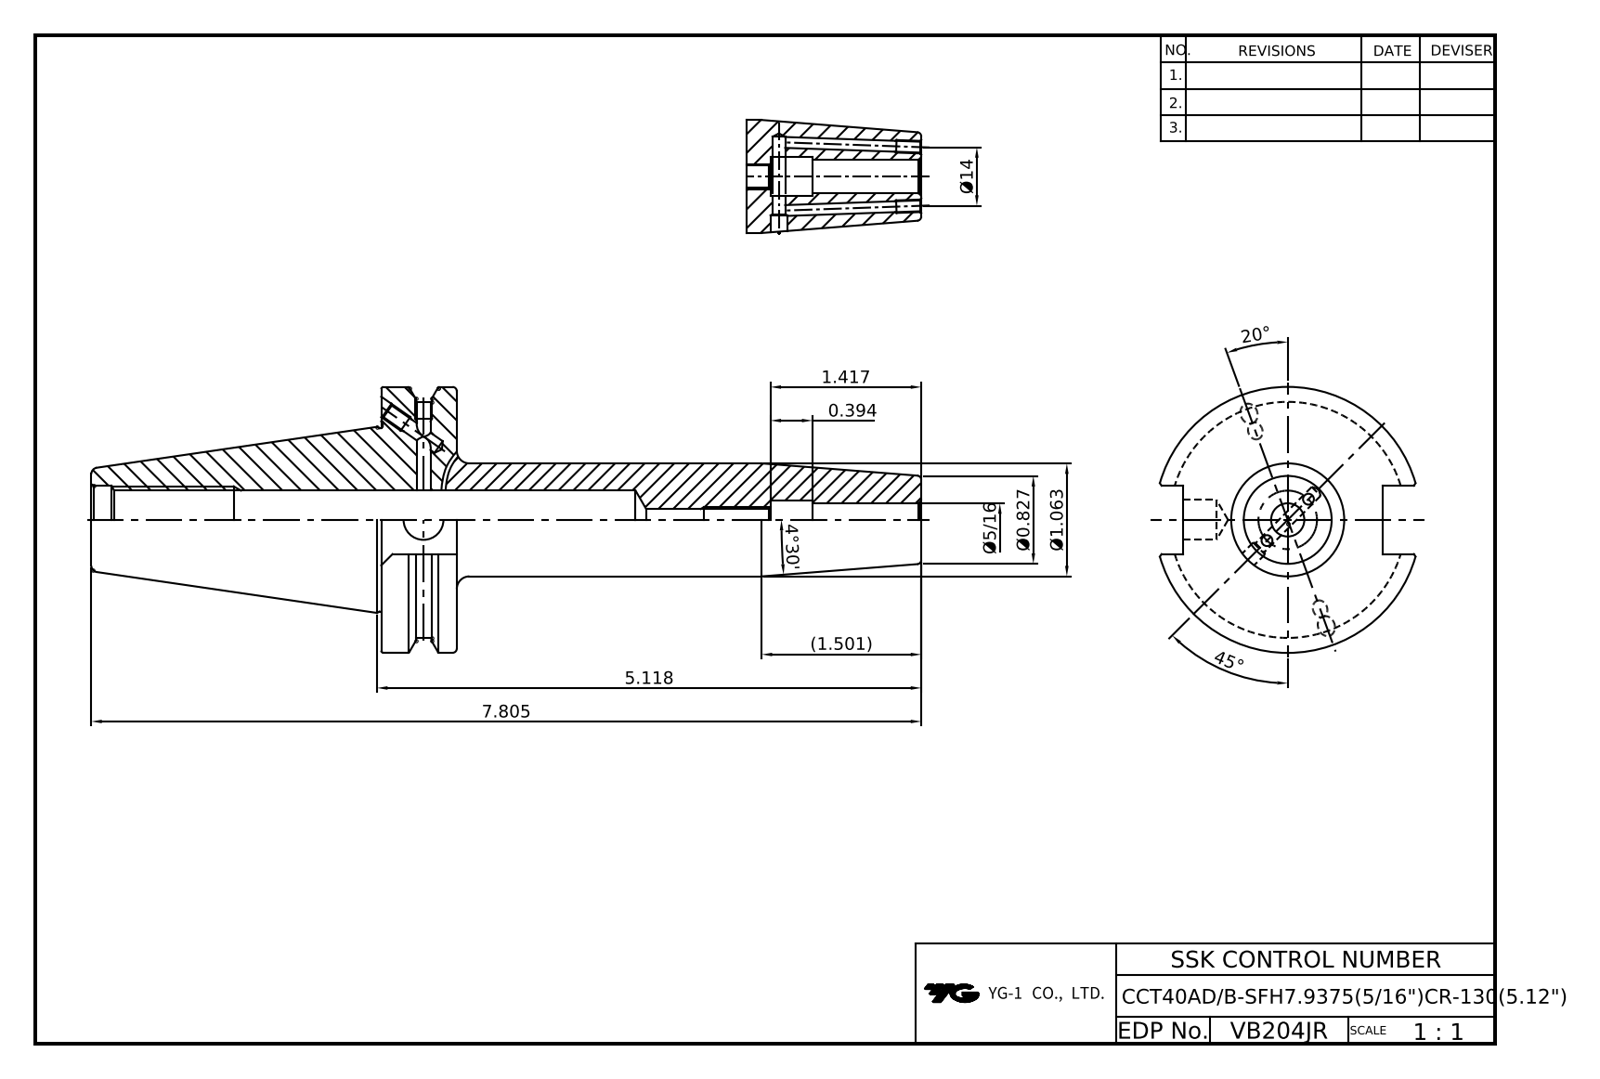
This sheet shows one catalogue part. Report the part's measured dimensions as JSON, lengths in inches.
{"part_name": "LO-CCT40ADB-SFH7.9375CR-130", "step_written_by": "Autodesk Inventor 2026 (AUTOMOTIVE_DESIGN)", "units": "inches", "bodies": {"solids": 1, "faces": 88, "planar": 37, "cylindrical": 29, "other": 22}, "overall_size": [7.805, 2.5, 2.405], "volume_in3": 9.379, "surface_area_in2": 52.04, "round_holes": [[0.128, 4], [0.097, 2], [0.157, 2], [0.165, 2], [0.194, 1], [0.313, 1], [0.358, 1], [0.375, 1], [0.527, 1], [0.642, 1]], "round_bosses_or_shafts": [[2.5, 1], [1.063, 1]], "partial_cylinders_radius": [[1.108, 1]], "face_to_face_distances": [0.711, 5.079, 4.368, 1.874, 0.645, 2.726, 3.437, 7.805, 3.201, 0.474]}
